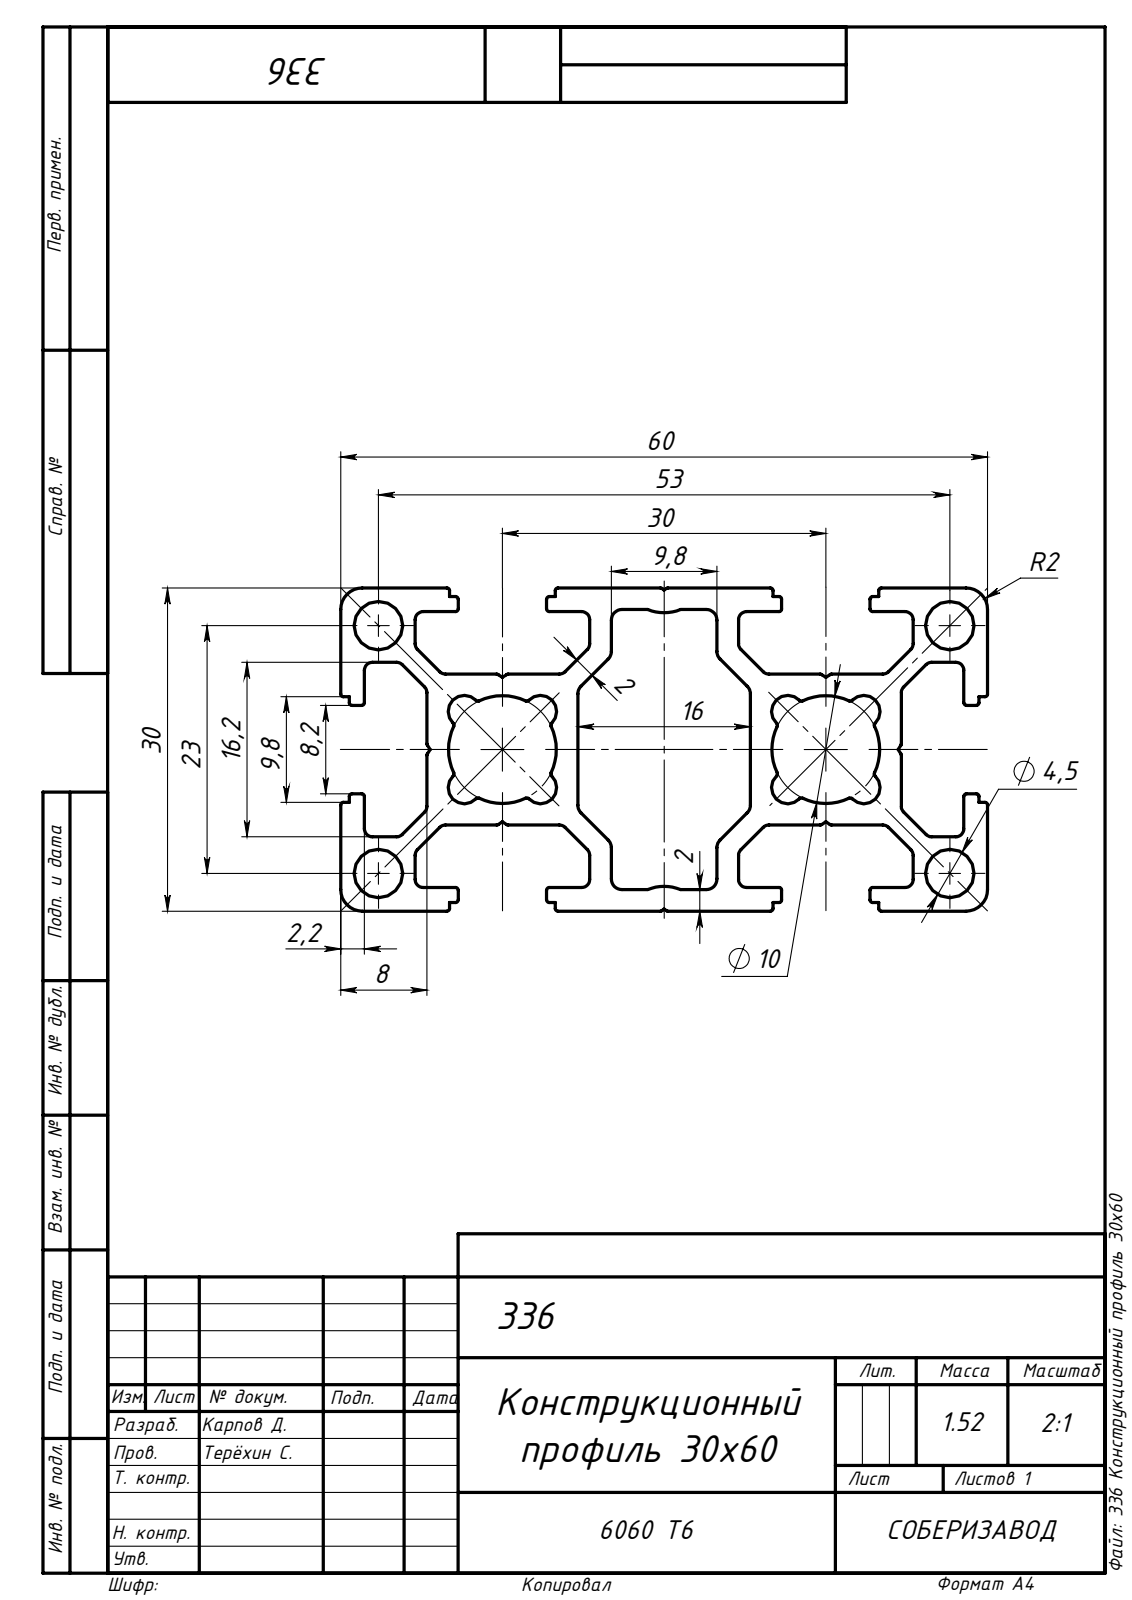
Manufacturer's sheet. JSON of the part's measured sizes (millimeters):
{"part_name": "336 Конструкционный профиль 30х60_00; Сборка1", "step_written_by": "SolidWorks 2021 (AUTOMOTIVE_DESIGN)", "units": "millimeters", "bodies": {"solids": 1, "faces": 402, "planar": 176, "cylindrical": 226, "other": 0}, "overall_size": [1000, 60, 30], "volume_mm3": 493473, "surface_area_mm2": 596490, "round_holes": [[4.5, 4]], "partial_cylinders_radius": [[0.25, 116], [0.75, 24], [0.3, 12], [1, 12], [2, 4], [4, 2], [5, 2]], "face_to_face_distances": [30, 22, 8, 15, 1.36, 12.64, 14, 2.2, 5.8, 19.8], "hole_center_spacings": [23, 53, 57.78]}
